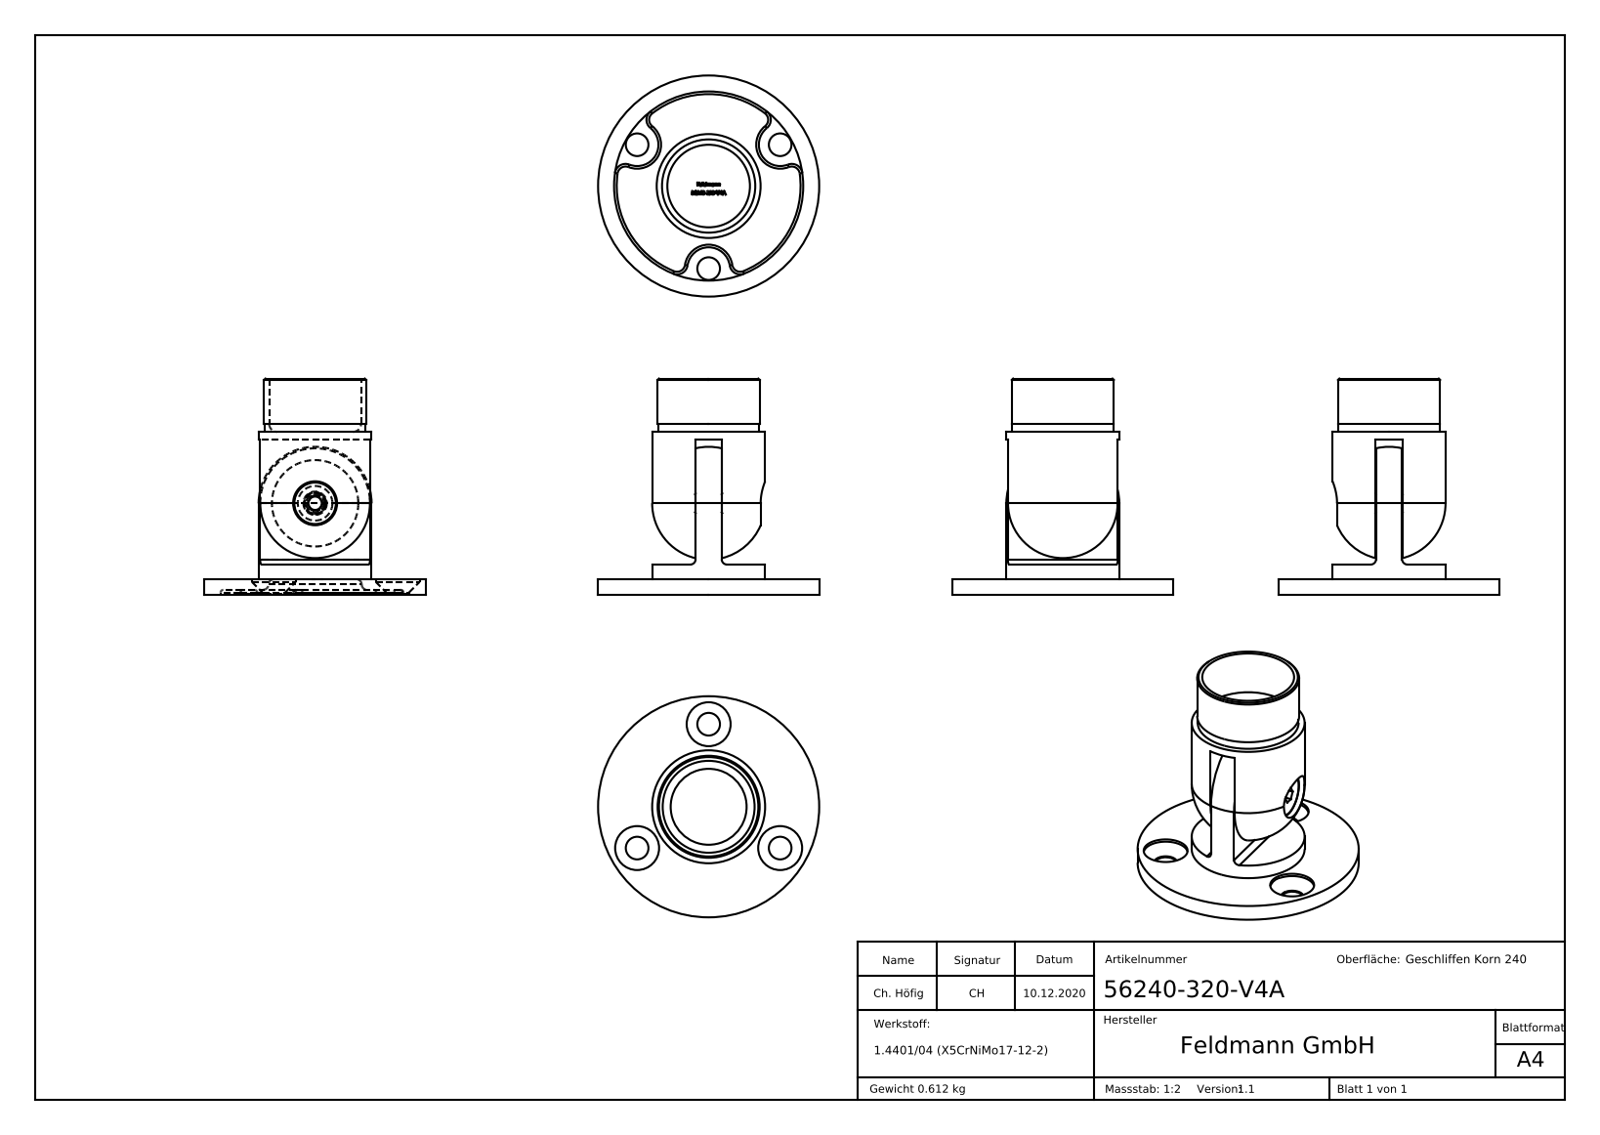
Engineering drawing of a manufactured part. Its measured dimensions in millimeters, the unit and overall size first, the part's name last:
Units: millimetres
Overall size (bounding box): 83 × 83 × 81.3
Round holes (diameter × count): ⌀16.5 ×4, ⌀8.5 ×3, ⌀6.8 ×1, ⌀8.2 ×1, ⌀34.5 ×1, ⌀71 ×1
Round bosses / shafts (diameter × count): ⌀83 ×1, ⌀42.4 ×1, ⌀38.3 ×1, ⌀37.9 ×1, ⌀15.57 ×1, ⌀13 ×1, ⌀8 ×1
Partial cylindrical surfaces — rounded edges, fillets, slot ends (radius × count): R4 ×6, R8 ×3, R2 ×2
Main face-to-face distances: 4, 10, 6, 9.8, 2, 5.5, 61.3, 59.3, 55.3, 11.5
Hole centre spacings: 31, 53.7
Volume: 77 888 mm³ · Surface area: 35 594 mm²
Bodies: 3 solids, 524 faces (193 planar, 91 cylindrical, 240 other)
Part name (STEP PRODUCT): 5624X-320 Teil2_56240-320-V4A Teil2; socket countersunk head screw_din_DIN 7991 - M8 x 30 --- 30S; socket countersunk head screw_din; 5624X-320 Teil2 (+3 more)
STEP written by: SolidWorks 2018 (CONFIG_CONTROL_DESIGN)
